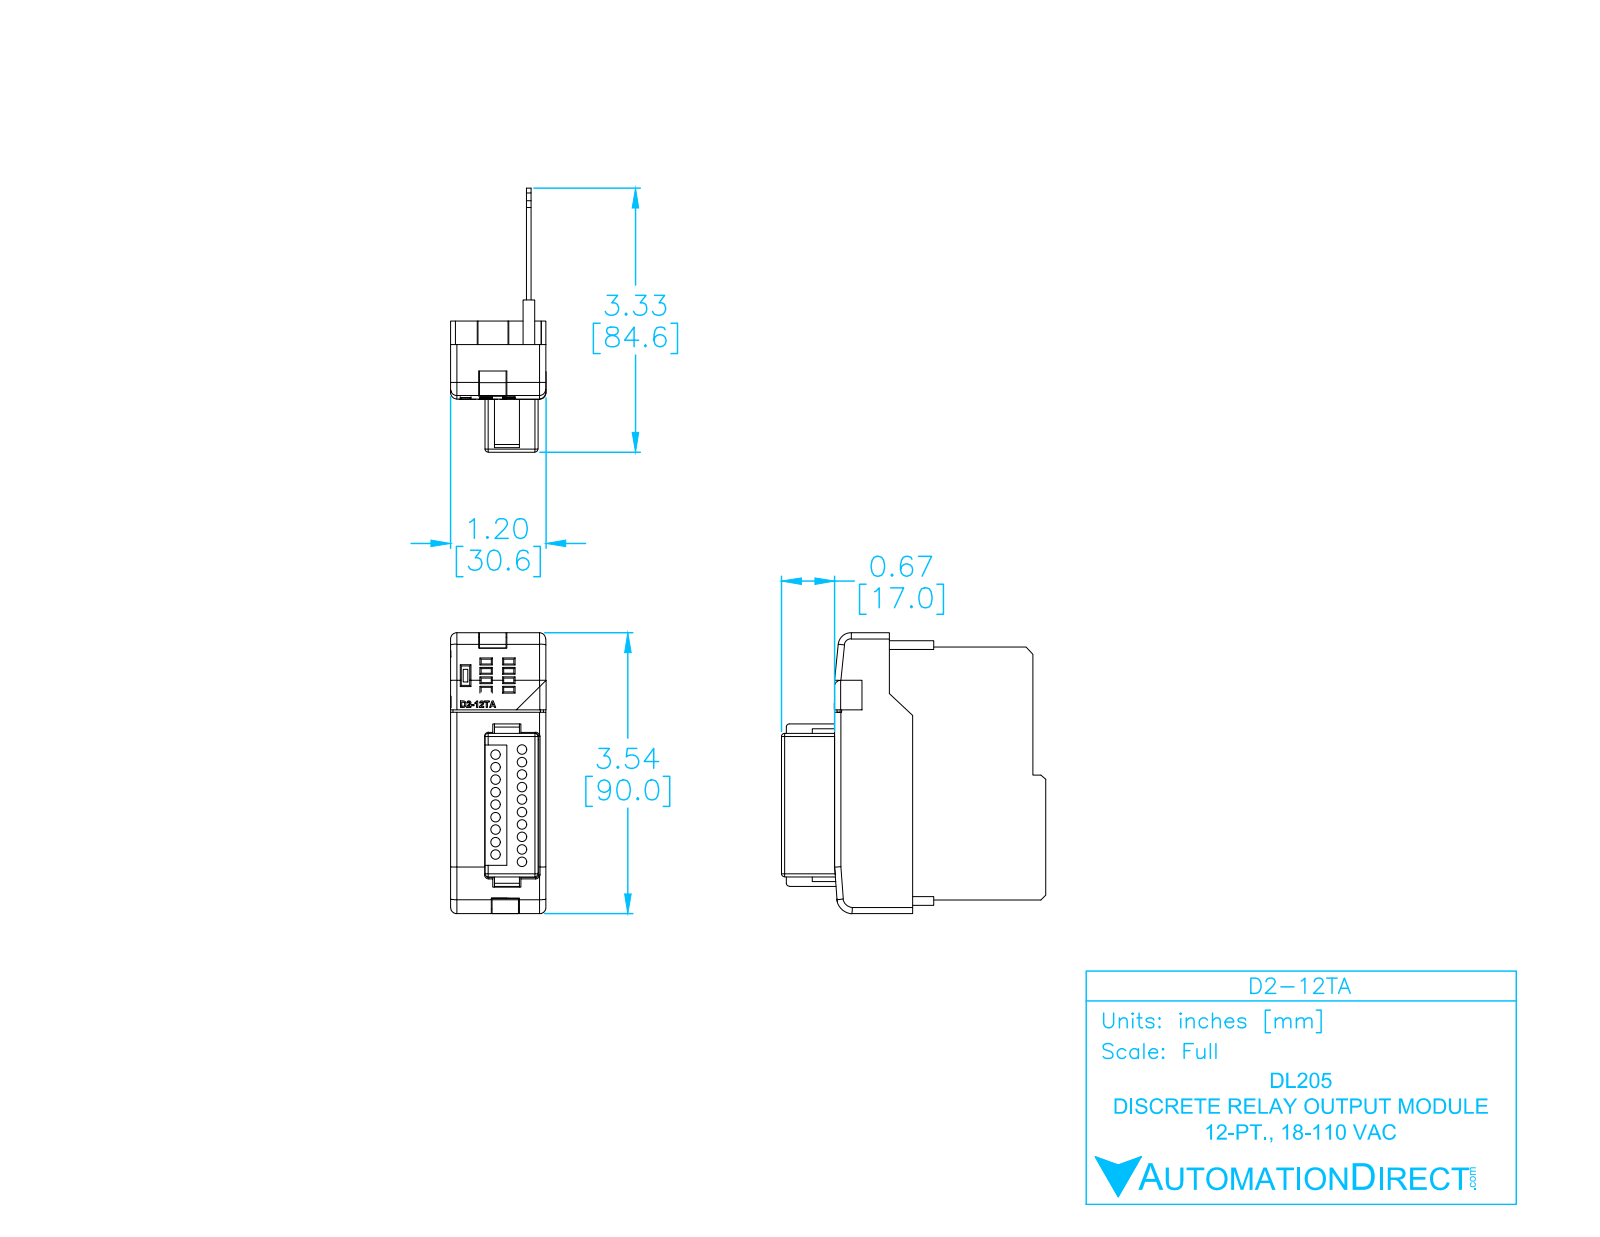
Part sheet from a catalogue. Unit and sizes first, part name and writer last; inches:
Units: inches
Overall size (bounding box): 3.543 × 3.331 × 1.203
Round holes (diameter × count): ⌀0.118 ×19
Partial cylindrical surfaces — rounded edges, fillets, slot ends (radius × count): R0.014 ×28, R0.039 ×18, R0.02 ×12, R0.079 ×11, R0.01 ×6, R0.103 ×1, R0.149 ×1, R0.162 ×1
Main face-to-face distances: 0.059, 0.186, 0.127, 0.245, 0.02, 0.039, 0.956, 1.142, 0.709, 0.433
Hole centre spacings: 0.157, 0.315, 0.472, 0.63, 0.339, 0.345, 0.787, 0.4
Volume: 1.865 in³ · Surface area: 50.54 in²
Bodies: 2 solids, 610 faces (403 planar, 158 cylindrical, 49 other)
Part name (STEP PRODUCT): D2-12TA_ModuleCase Light_NEW
STEP written by: SolidWorks 2009 (AUTOMOTIVE_DESIGN)
